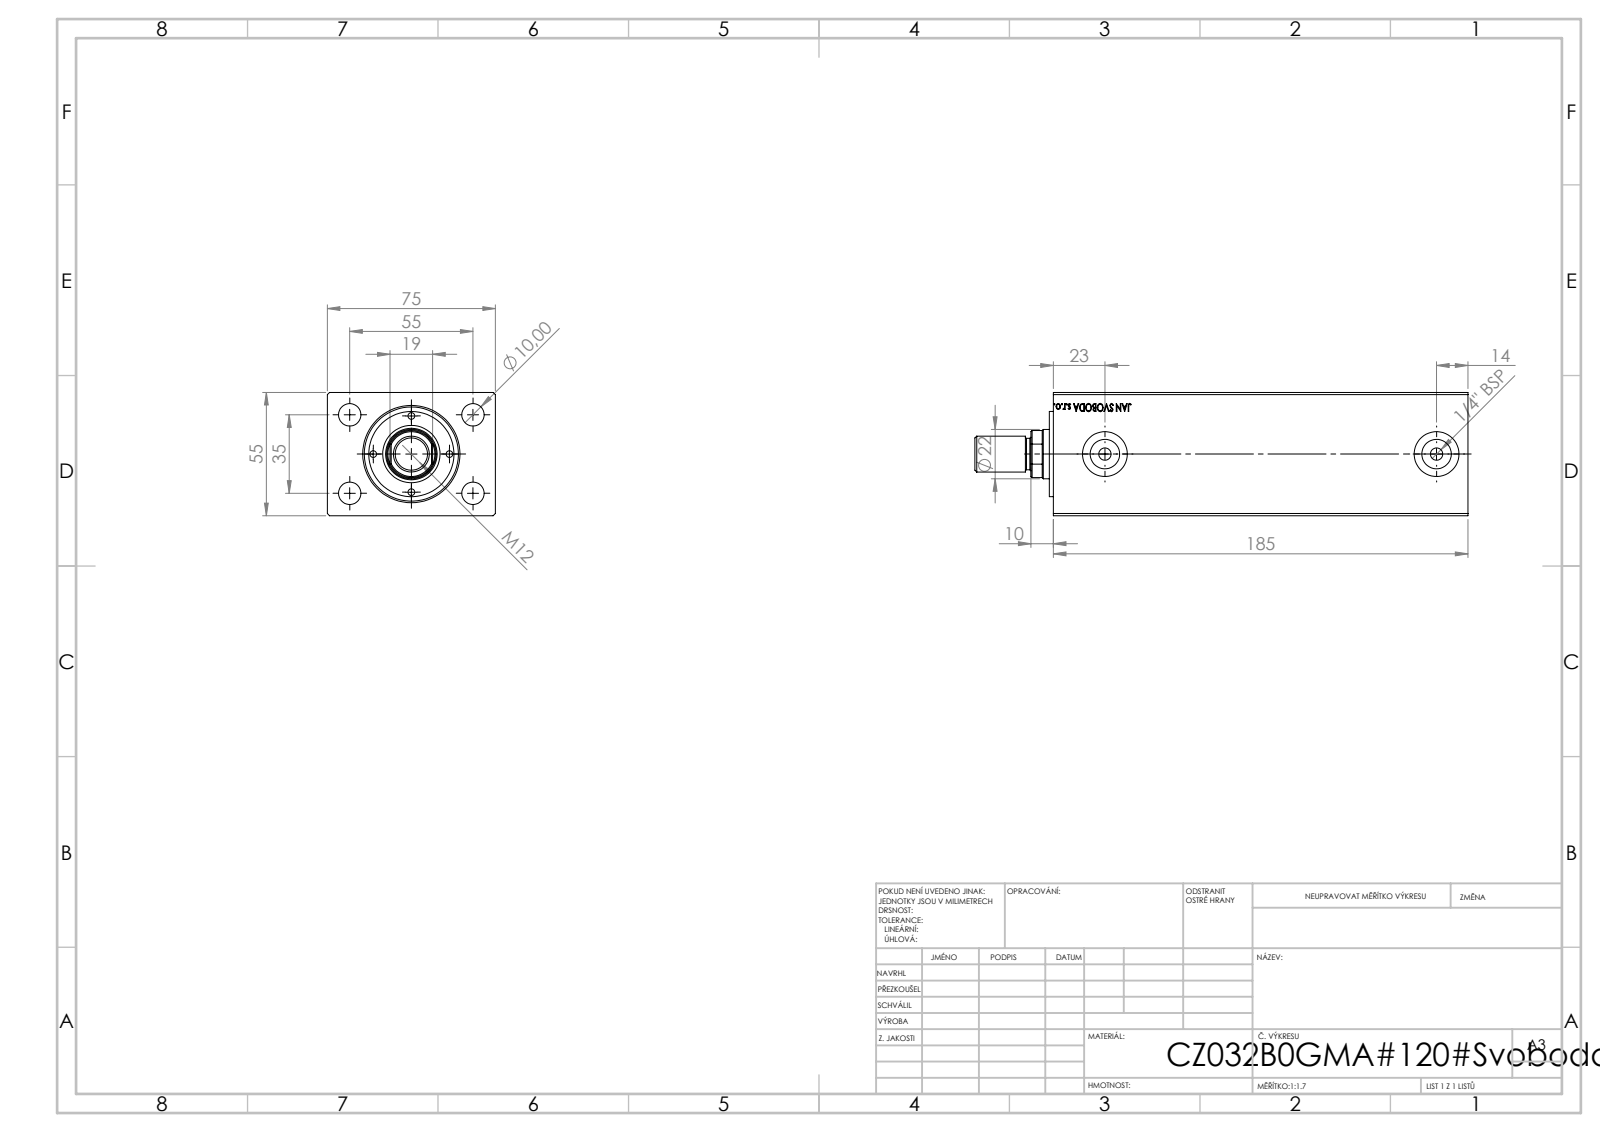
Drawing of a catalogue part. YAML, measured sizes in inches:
part_name: "V500CZ_B_VC; V500CZ; V500CZ_MALE_METRIC"
step_written_by: "SolidWorks 2019 (CONFIG_CONTROL_DESIGN)"
units: inches
bodies: {solids: 4, faces: 887, planar: 403, cylindrical: 62, other: 422}
overall_size: [8.661, 2.953, 2.165]
volume: 42.59
surface_area: 159.3
round_holes:
  - {diameter: 0.118, count: 4}
  - {diameter: 0.394, count: 4}
  - {diameter: 0.217, count: 2}
  - {diameter: 0.518, count: 2}
  - {diameter: 0.787, count: 2}
  - {diameter: 0.413, count: 1}
  - {diameter: 0.866, count: 1}
  - {diameter: 0.906, count: 1}
  - {diameter: 1.26, count: 1}
  - {diameter: 1.417, count: 1}
  - {diameter: 1.654, count: 1}
round_bosses_or_shafts:
  - {diameter: 1.496, count: 1}
  - {diameter: 0.63, count: 1}
  - {diameter: 0.551, count: 1}
partial_cylinders:
  - {radius: 0.413, count: 1}
face_to_face_distances: [2.165, 2.953, 7.283, 6.74, 0.543, 0.394, 0.323, 0.071, 7.276, 0.535]
hole_center_spacings: [0.669, 0.804, 0.946, 1.083, 1.283, 1.737, 1.883, 1.339]
